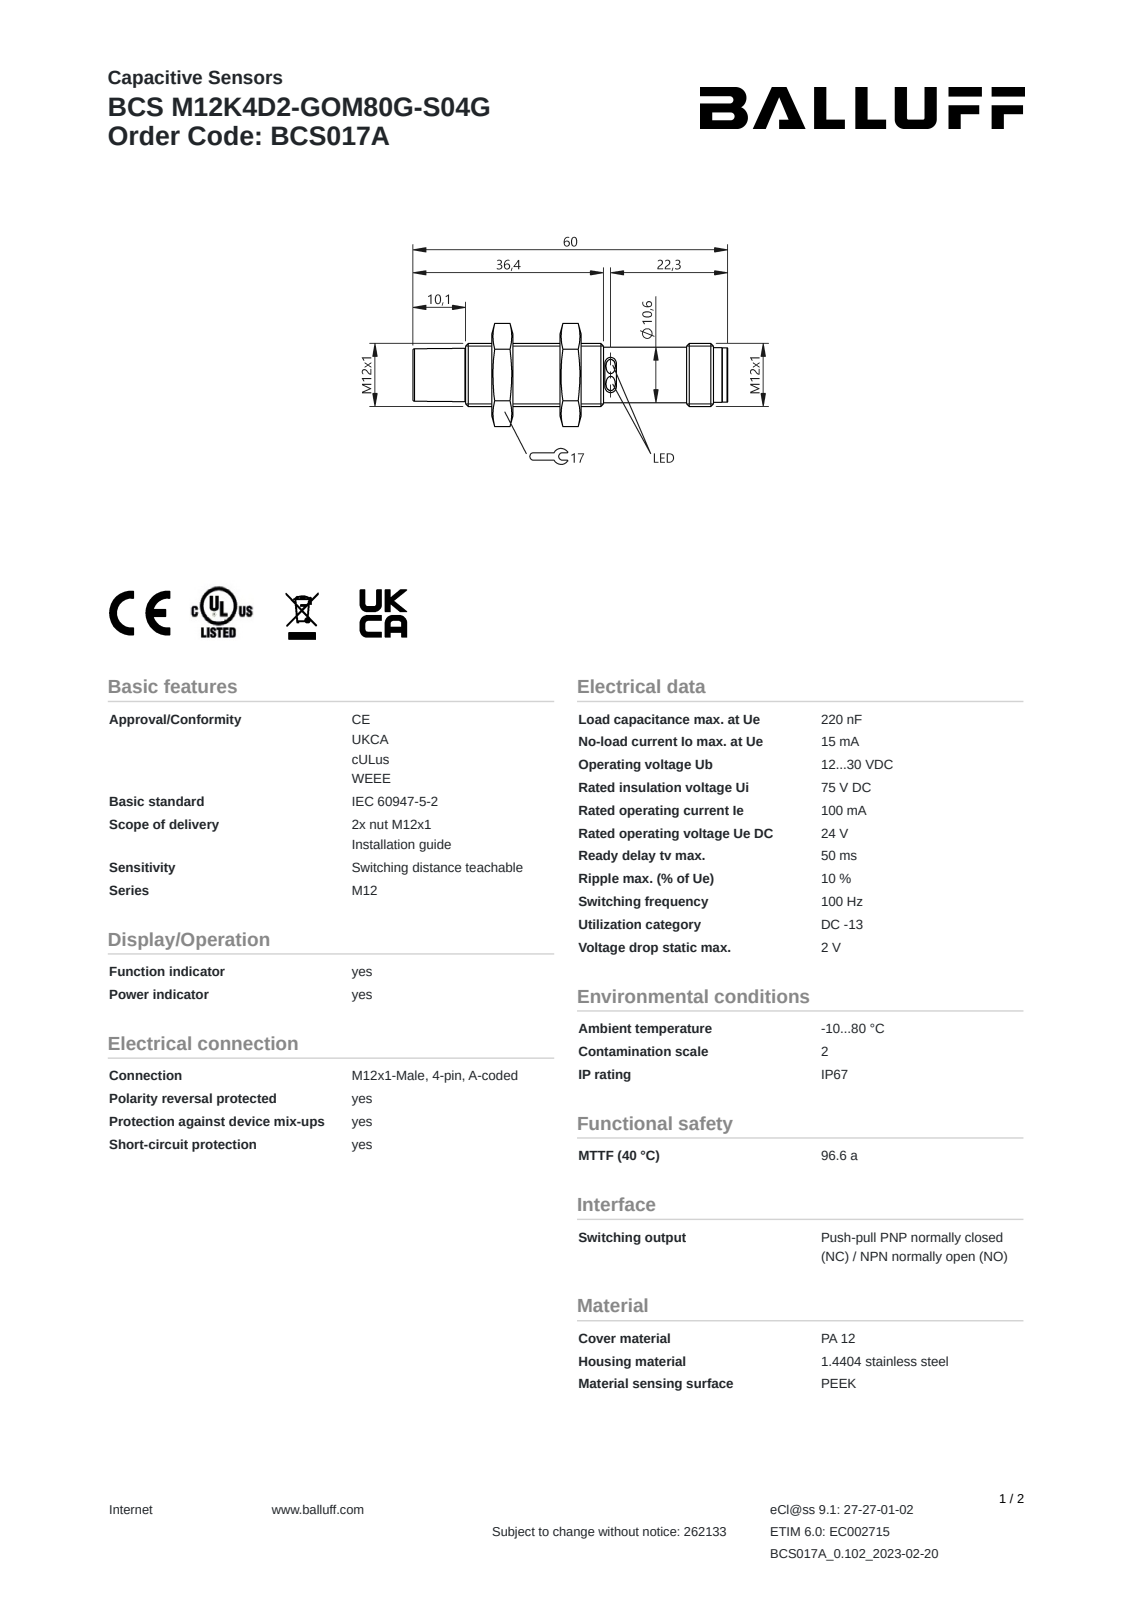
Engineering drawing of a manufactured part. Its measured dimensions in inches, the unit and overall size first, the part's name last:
Units: inches
Overall size (bounding box): 2.362 × 0.773 × 0.669
Round holes (diameter × count): ⌀0.331 ×1, ⌀0.43 ×1
Round bosses / shafts (diameter × count): ⌀0.039 ×4, ⌀0.472 ×1, ⌀0.417 ×1, ⌀0.407 ×1, ⌀0.386 ×1
Partial cylindrical surfaces — rounded edges, fillets, slot ends (radius × count): R0.028 ×4, R0.075 ×4, R0.012 ×2, R0.043 ×2, R0.024 ×1, R0.18 ×1, R0.182 ×1
Main face-to-face distances: 0.516, 0.157, 0.669, 0.673, 0.358, 1.264, 1.106, 0.748, 0.591, 0.752
Volume: 0.407 in³ · Surface area: 6.149 in²
Bodies: 3 solids, 111 faces (38 planar, 30 cylindrical, 43 other)
Part name (STEP PRODUCT): BCS017A
STEP written by: SolidWorks 2021 (AUTOMOTIVE_DESIGN)
